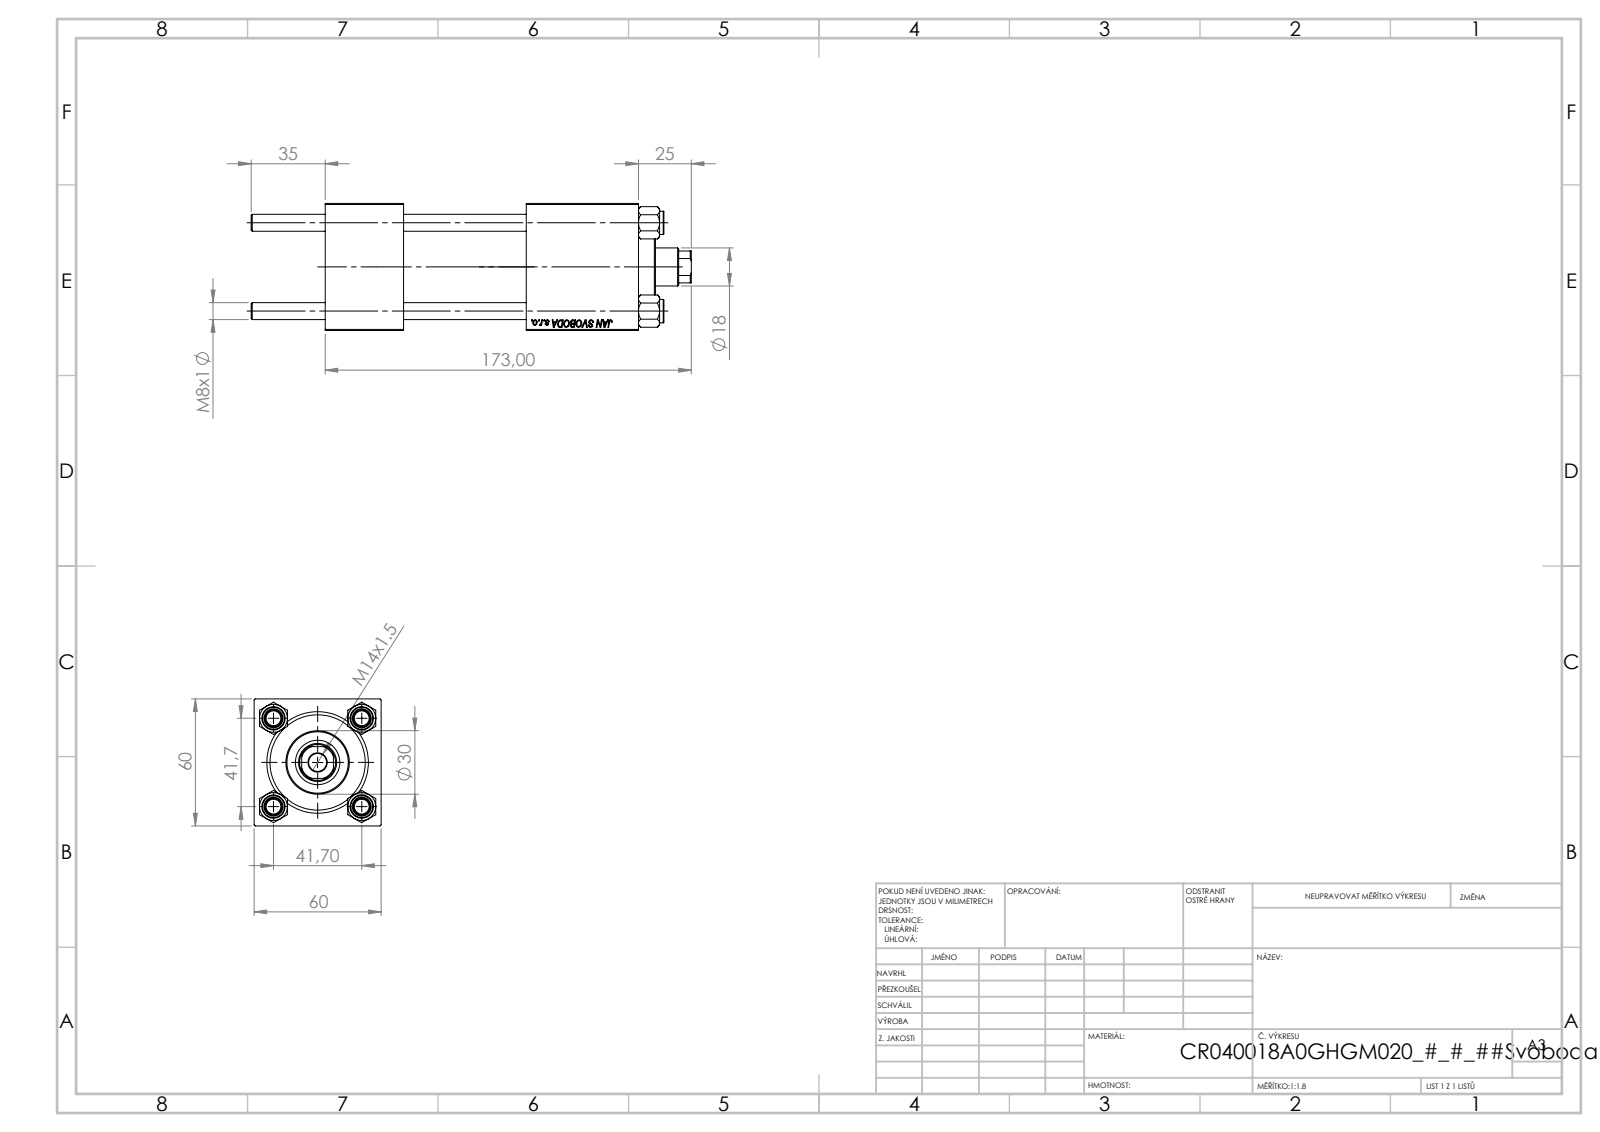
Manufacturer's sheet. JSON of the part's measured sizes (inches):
{"part_name": "NUT_M5; V215_VC_A; V215CR_BODY_A; CR025_012_A_0_G_A_G_M_020_+#_##_TYCINKA (+1 more)", "step_written_by": "SolidWorks 2019 (CONFIG_CONTROL_DESIGN)", "units": "inches", "bodies": {"solids": 11, "faces": 1135, "planar": 521, "cylindrical": 78, "other": 536}, "overall_size": [8.189, 2.362, 2.362], "volume_in3": 25.26, "surface_area_in2": 176.7, "round_holes": [[0.315, 4], [0.276, 2], [0.656, 2], [0.945, 2], [0.335, 1], [0.709, 1], [0.827, 1], [1.22, 1], [1.575, 1], [1.772, 1]], "round_bosses_or_shafts": [[0.433, 4], [1.811, 1], [1.181, 1]], "partial_cylinders_radius": [[0.335, 1]], "face_to_face_distances": [2.362, 1.457, 5.827, 4.37, 2.283, 2.087, 3.74, 4.697, 3.24, 0.957], "hole_center_spacings": [1.161, 1.642, 2.322, 3.642]}
